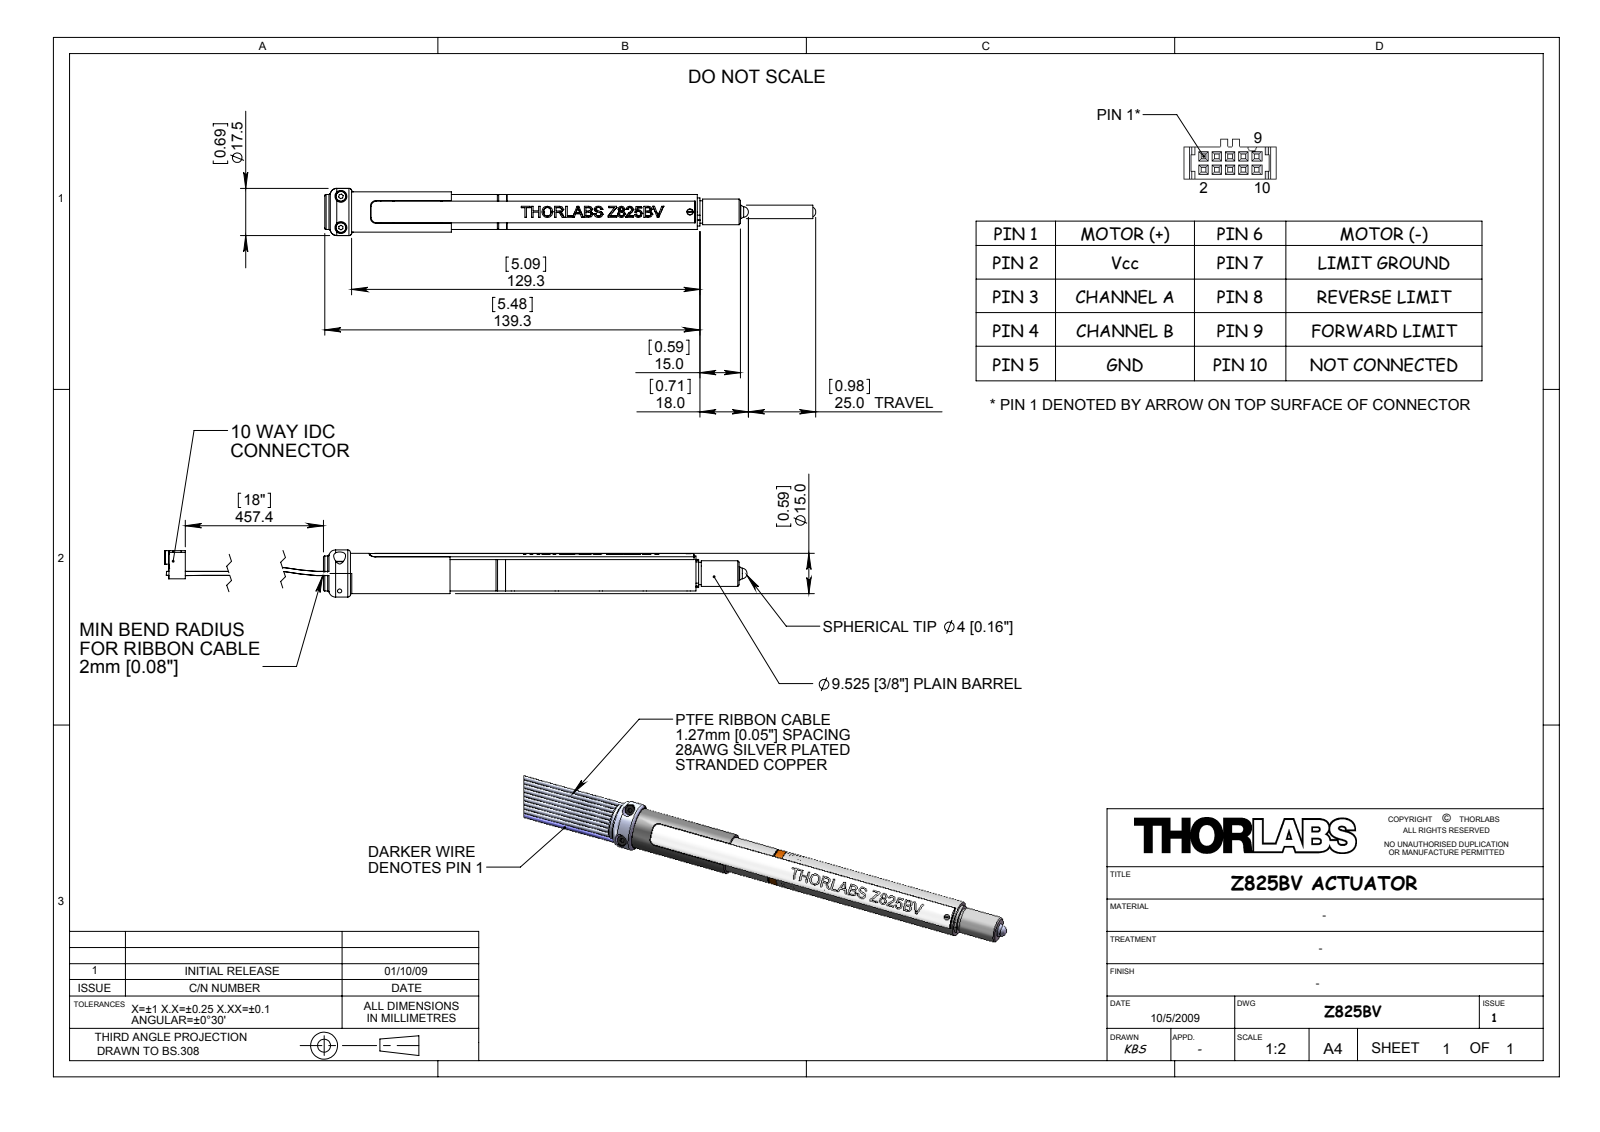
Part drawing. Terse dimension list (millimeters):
name: Z825BV
written by: SolidWorks 2007 (AUTOMOTIVE_DESIGN)
unit: mm
bodies: 0 solids, 178 faces (40 planar, 94 cylindrical, 44 other)
size: 157.29 × 17.5 × 17.5
holes: 2× ⌀1.6, 2× ⌀4.4, 1× ⌀1.2
bosses: 2× ⌀3.8, 1× ⌀17.5, 1× ⌀15, 1× ⌀13, 1× ⌀12.8, 1× ⌀10.5, 1× ⌀9.53, 1× ⌀8.3
rounds: 4× R2, 2× R1.5, 1× R7.4, 1× R7.41
face distances: 8, 1.1, 10, 1, 138.3, 128.3, 154.3, 144.3, 16, 47
hole spacings: 129.73, 11.6
